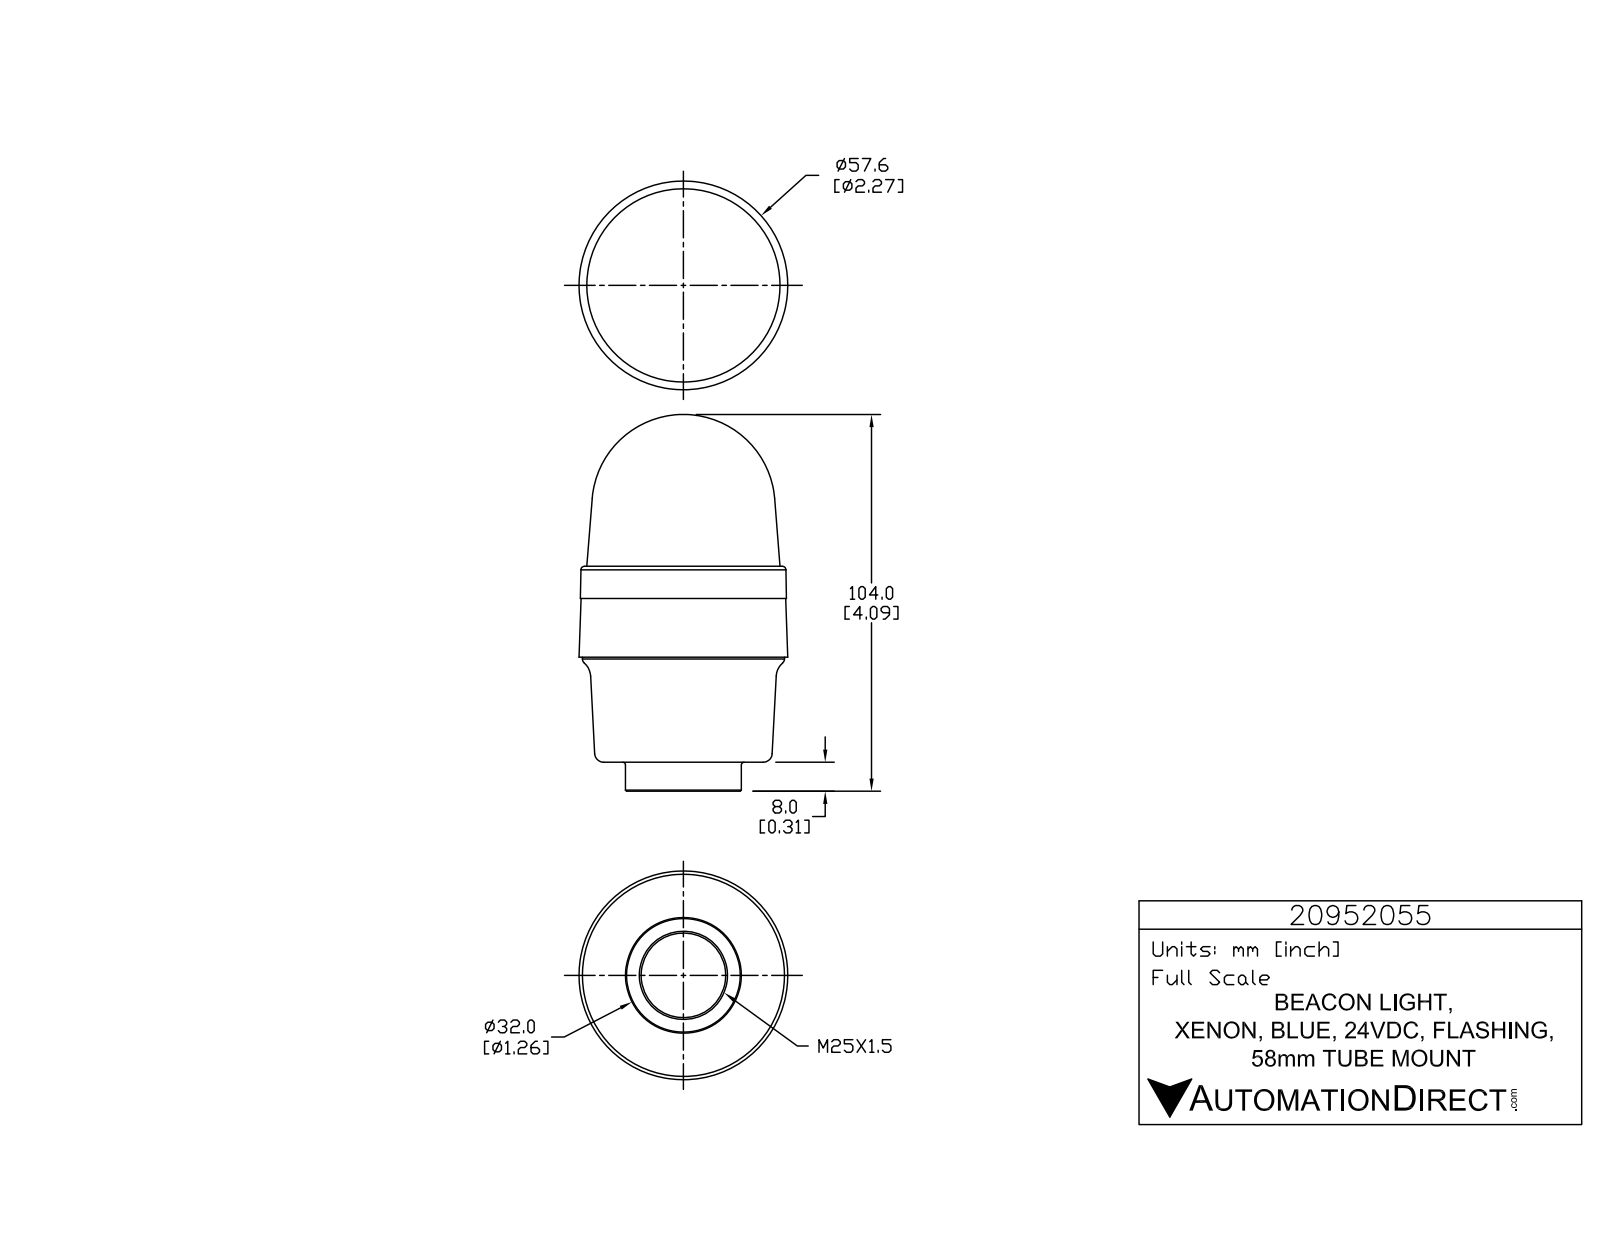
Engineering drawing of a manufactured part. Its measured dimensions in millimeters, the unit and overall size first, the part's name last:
Units: millimetres
Overall size (bounding box): 102.9 × 57.6 × 57.6
Round holes (diameter × count): ⌀1 ×3, ⌀23.4 ×1
Round bosses / shafts (diameter × count): ⌀5.7 ×3, ⌀1.4 ×3, ⌀55.8 ×1, ⌀32 ×1
Partial cylindrical surfaces — rounded edges, fillets, slot ends (radius × count): R0.2 ×6, R0.2 ×6, R0.2 ×6, R3.3 ×6, R0.1 ×3, R0.1 ×3, R0.2 ×3, R0.2 ×3
Main face-to-face distances: 8, 29, 37, 25.1, 54.1, 62.1, 8.9, 16.2, 45.2, 53.2
Volume: 192 100 mm³ · Surface area: 19 310 mm²
Bodies: 1 solid, 791 faces (525 planar, 168 cylindrical, 98 other)
Part name (STEP PRODUCT): 20952055
STEP written by: SolidWorks 2015 (AUTOMOTIVE_DESIGN)
